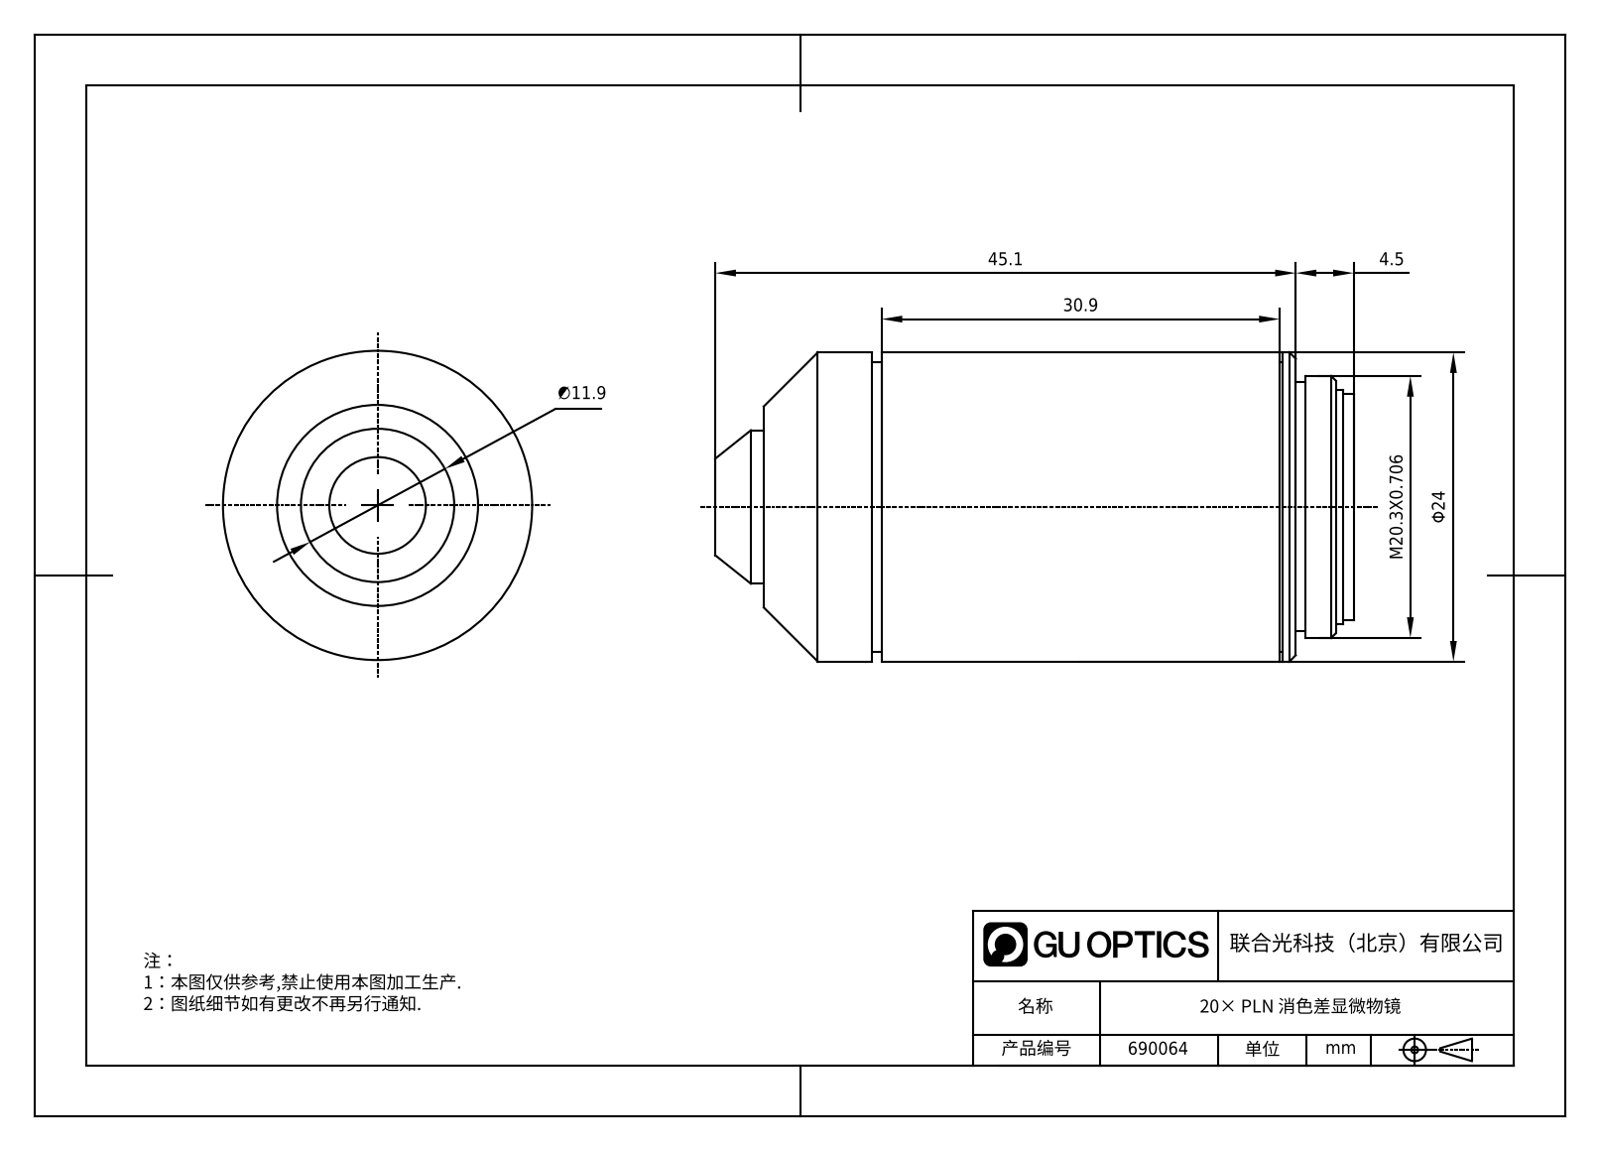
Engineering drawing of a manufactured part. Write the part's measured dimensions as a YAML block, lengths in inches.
part_name: "690064"
step_written_by: "SolidWorks 2020 (CONFIG_CONTROL_DESIGN)"
units: inches
bodies: {solids: 1, faces: 39, planar: 11, cylindrical: 20, other: 8}
overall_size: [1.909, 0.945, 0.945]
volume: 1.197
surface_area: 6.78
round_bosses_or_shafts:
  - {diameter: 0.945, count: 1}
  - {diameter: 0.886, count: 1}
  - {diameter: 0.8, count: 1}
  - {diameter: 0.761, count: 1}
  - {diameter: 0.69, count: 1}
  - {diameter: 0.67, count: 1}
  - {diameter: 0.469, count: 1}
face_to_face_distances: [0.189, 1.299, 0.03, 1.626, 1.815, 0.327, 1.577, 1.25, 1.488, 0.049]
